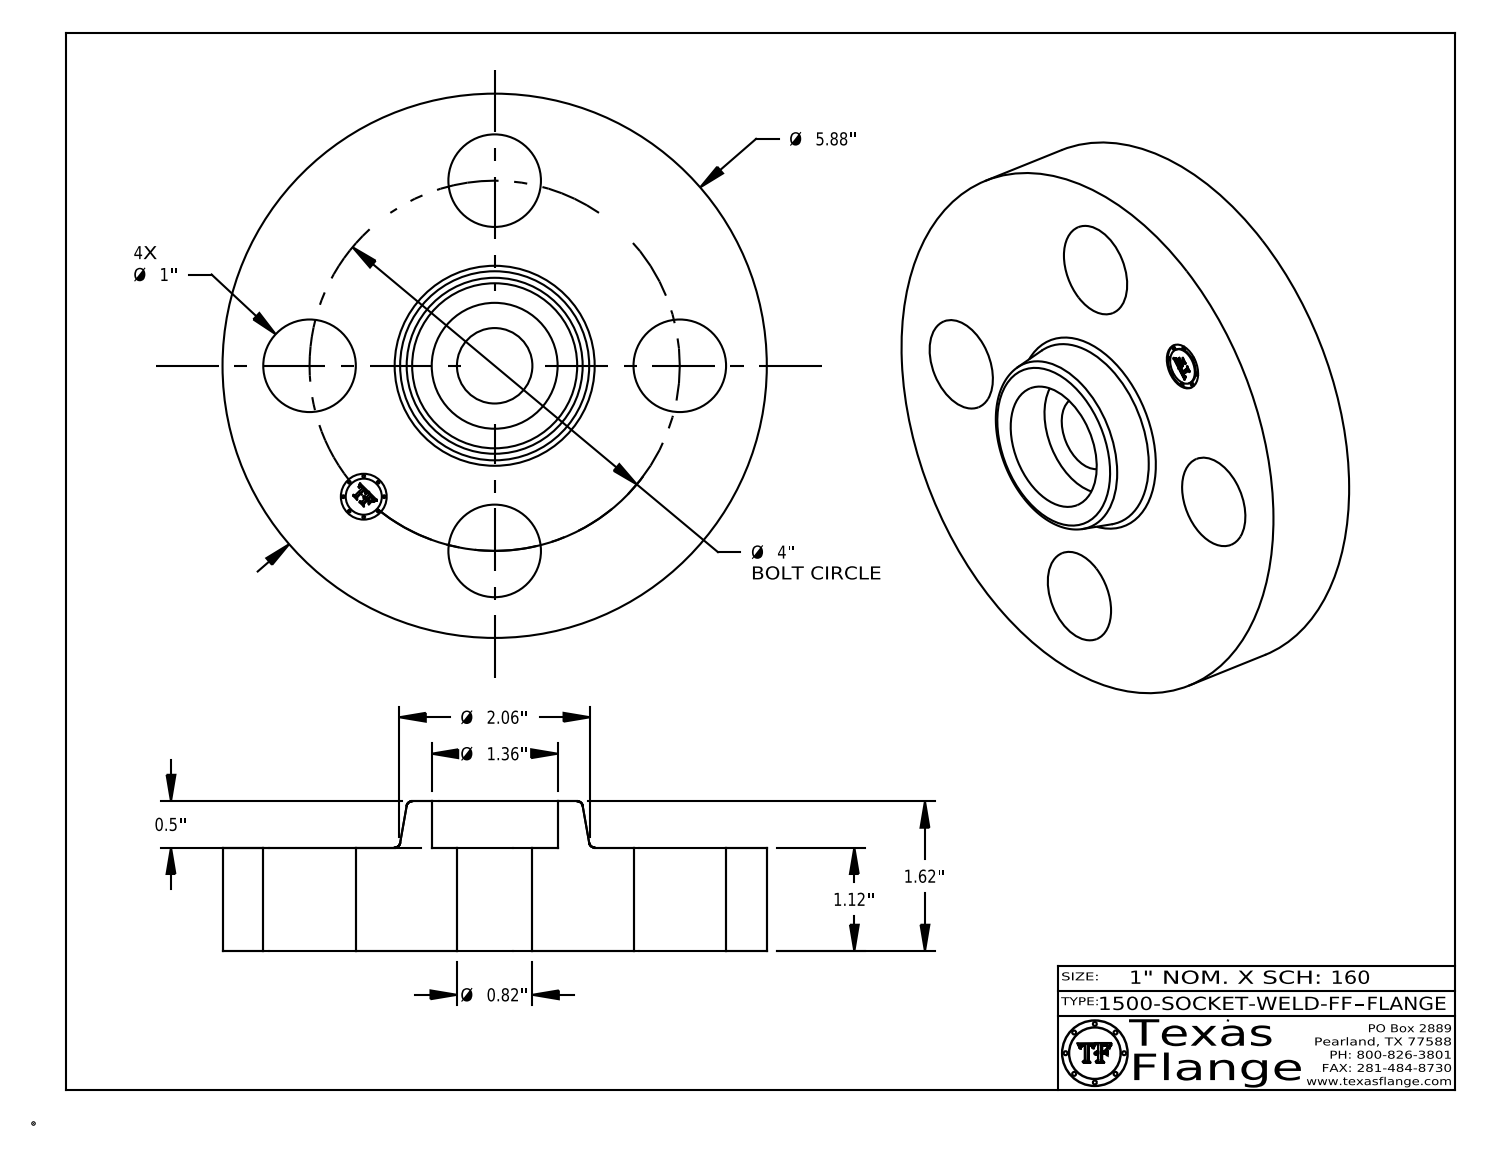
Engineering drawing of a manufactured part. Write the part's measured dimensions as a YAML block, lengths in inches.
part_name: "1500-SOCKET-WELD-FF"
step_written_by: "CATIA V5 STEP AP214 (AUTOMOTIVE_DESIGN)"
units: inches
bodies: {solids: 1, faces: 409, planar: 369, cylindrical: 34, other: 6}
overall_size: [5.88, 5.88, 1.62]
volume: 27.11
surface_area: 89.23
round_holes:
  - {diameter: 1, count: 4}
  - {diameter: 0.495, count: 1}
  - {diameter: 0.815, count: 1}
  - {diameter: 1.36, count: 1}
round_bosses_or_shafts:
  - {diameter: 0.03, count: 8}
  - {diameter: 5.88, count: 1}
  - {diameter: 0.39, count: 1}
face_to_face_distances: [1.12, 1.62, 0.5, 0.015, 1.105, 0.515, 0.148, 0.145, 0.027, 0.096]
hole_center_spacings: [2, 2.828, 1.531, 3.695, 4]
